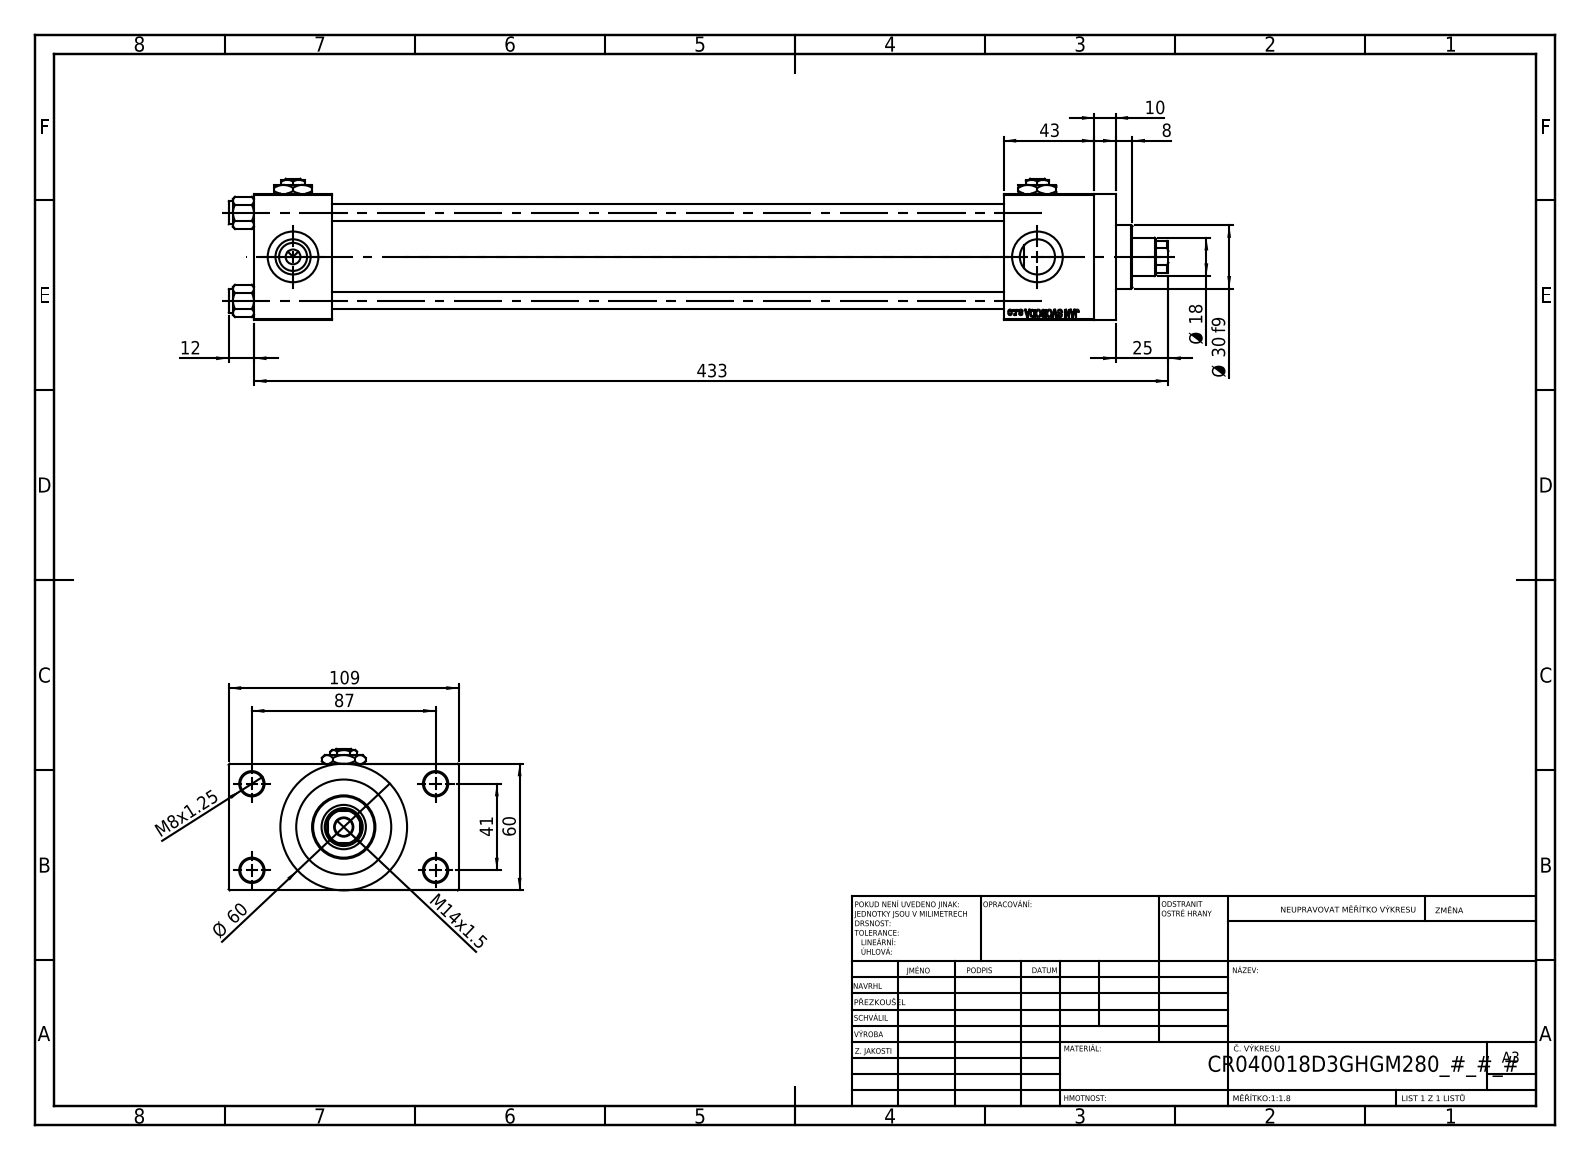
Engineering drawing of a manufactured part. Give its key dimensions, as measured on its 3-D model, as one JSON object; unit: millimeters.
{"part_name": "V215CR_D_Body; V215CR_VCP_D; V215_VC_A; Zatka_pro_OIL_PORT (+2 more)", "step_written_by": "SolidWorks 2019 (CONFIG_CONTROL_DESIGN)", "units": "millimeters", "bodies": {"solids": 13, "faces": 1205, "planar": 546, "cylindrical": 99, "other": 560}, "overall_size": [445, 109, 67], "volume_mm3": 734144, "surface_area_mm2": 236279, "round_holes": [[8, 4], [11, 4], [16.66, 4], [24, 4], [7, 3], [8.5, 1], [18, 1], [21, 1], [31, 1], [40, 1], [45, 1]], "round_bosses_or_shafts": [[11, 4], [60, 1], [46, 1], [30, 1]], "partial_cylinders_radius": [[8.5, 1]], "face_to_face_distances": [60, 318, 24.5, 84.5, 37, 355, 43, 398, 361, 10], "hole_center_spacings": [22.65, 29.49, 41.7, 47.15, 48.09, 64.35, 76.49, 41]}
